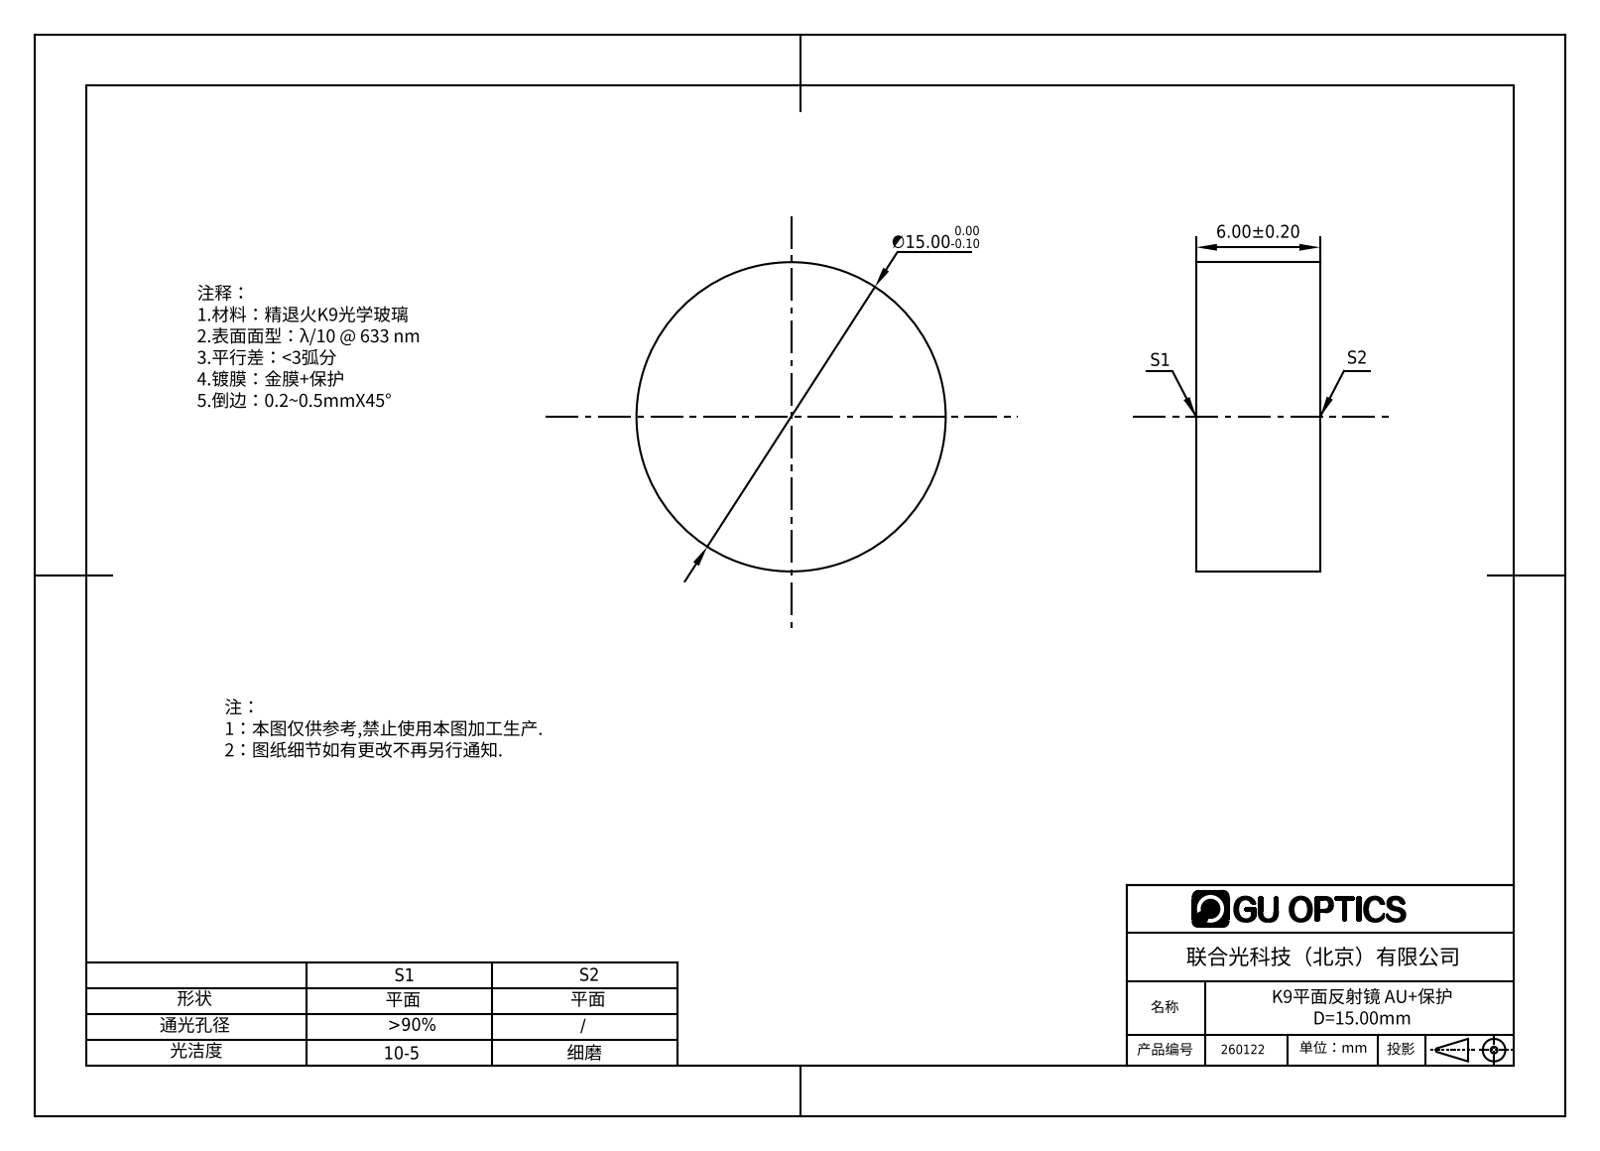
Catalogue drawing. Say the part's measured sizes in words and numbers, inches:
The part is named "260070". Its 3-D file was written by "SolidWorks 2016 (AUTOMOTIVE_DESIGN)". It is 1 solid with 4 faces: 2 planar, 2 cylindrical and 0 other. Overall it measures 0.591 by 0.591 by 0.236 inches. Its volume is 0.065 cubic inches and its surface area 0.986 square inches. Round bosses or shafts: 1 of diameter 0.591. The main face-to-face distances are 0.236.
